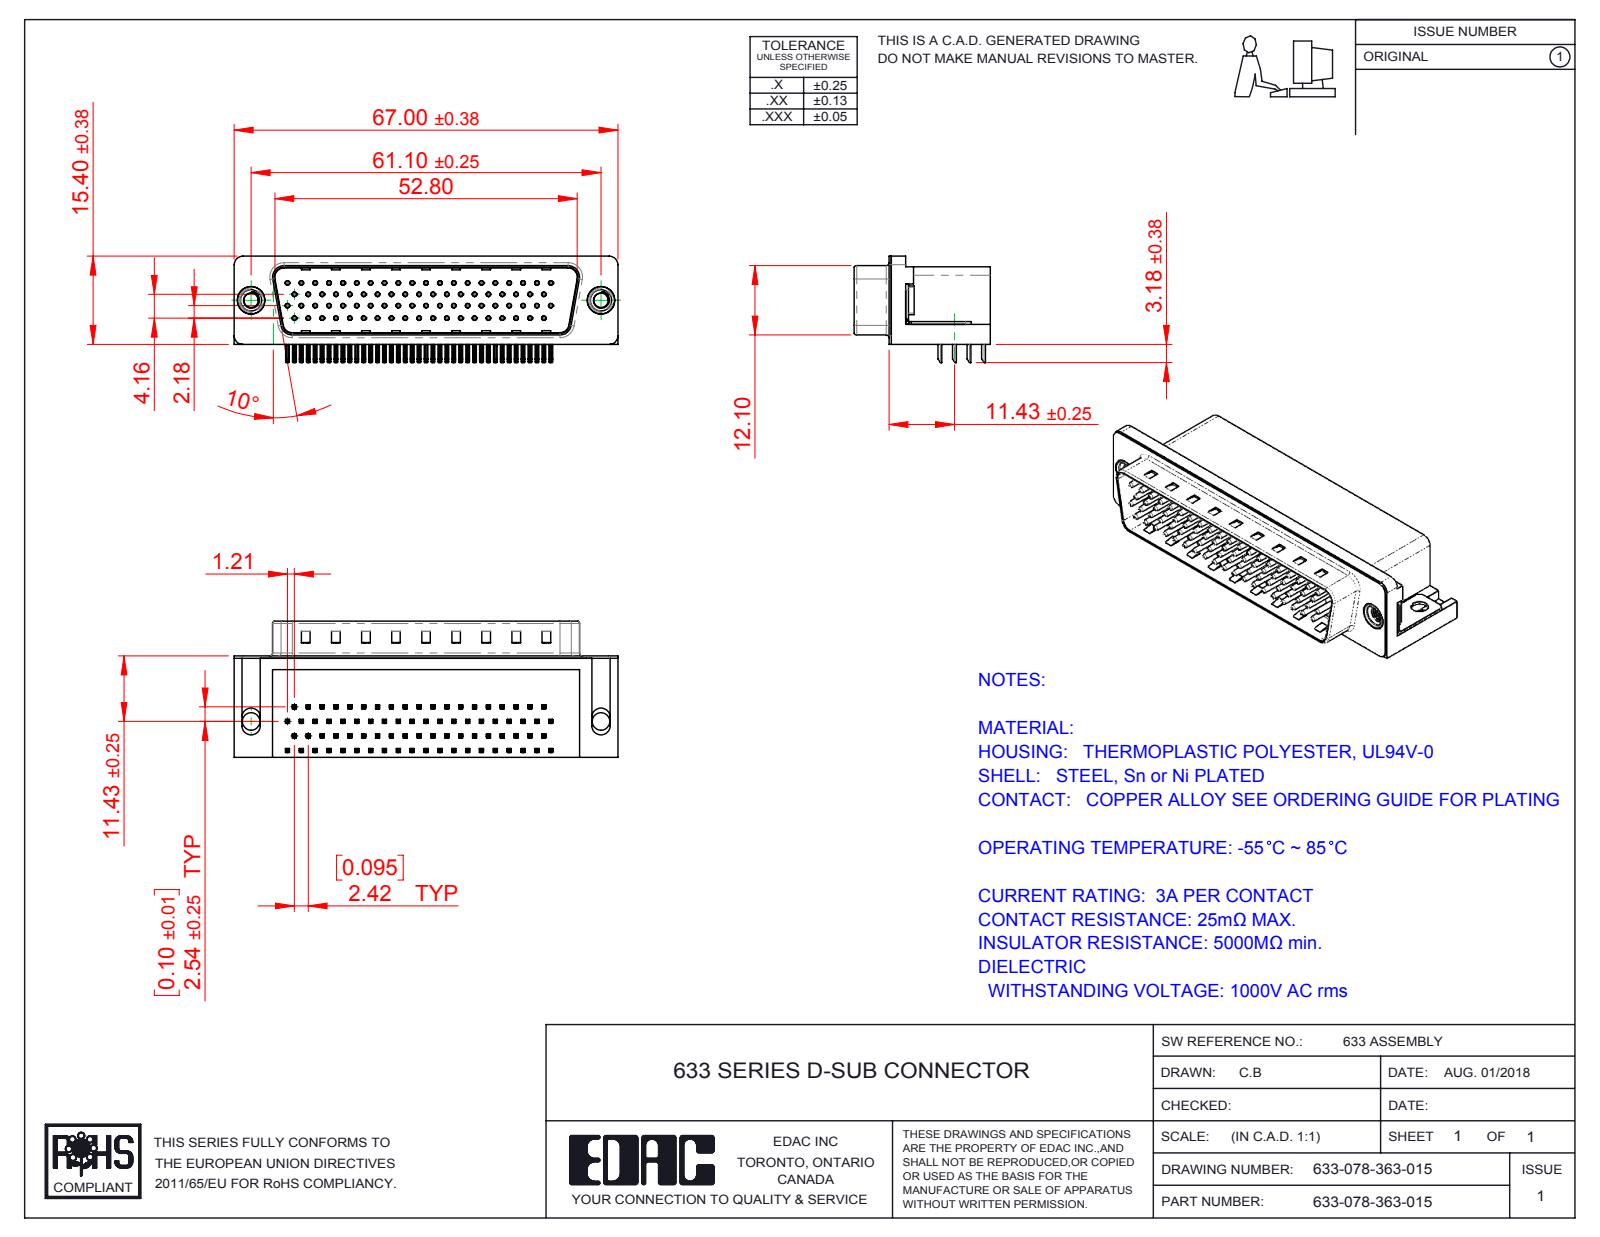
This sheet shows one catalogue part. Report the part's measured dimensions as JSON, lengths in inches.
{"part_name": "633 Thru Hole Board Mount_78 Contact; 633 Contact Top 78; 633 Contact Top_78 Contact; 633 Contact Middle_78 Contact (+5 more)", "step_written_by": "SolidWorks 2016 (CONFIG_CONTROL_DESIGN)", "units": "inches", "bodies": {"solids": 84, "faces": 6274, "planar": 3979, "cylindrical": 1782, "other": 513}, "overall_size": [2.638, 0.937, 0.731], "volume_in3": 0.891, "surface_area_in2": 25.33, "round_holes": [[0.014, 78], [0.031, 78], [0.098, 2], [0.12, 2], [0.157, 2], [0.189, 2], [0.197, 2]], "round_bosses_or_shafts": [[0.03, 78], [0.193, 2], [0.187, 2], [0.154, 2]], "partial_cylinders_radius": [[0.01, 320], [0.005, 156], [0.039, 16], [0.02, 9], [0.063, 8], [0.059, 6], [0.018, 4], [0.035, 4]], "face_to_face_distances": [0.016, 0.52, 0.681, 0.461, 0.526, 0.081, 0.541, 0.065, 0.073, 0.469], "hole_center_spacings": [0.095, 0.191, 0.286, 0.381, 0.246, 0.281, 0.476, 0.339]}
